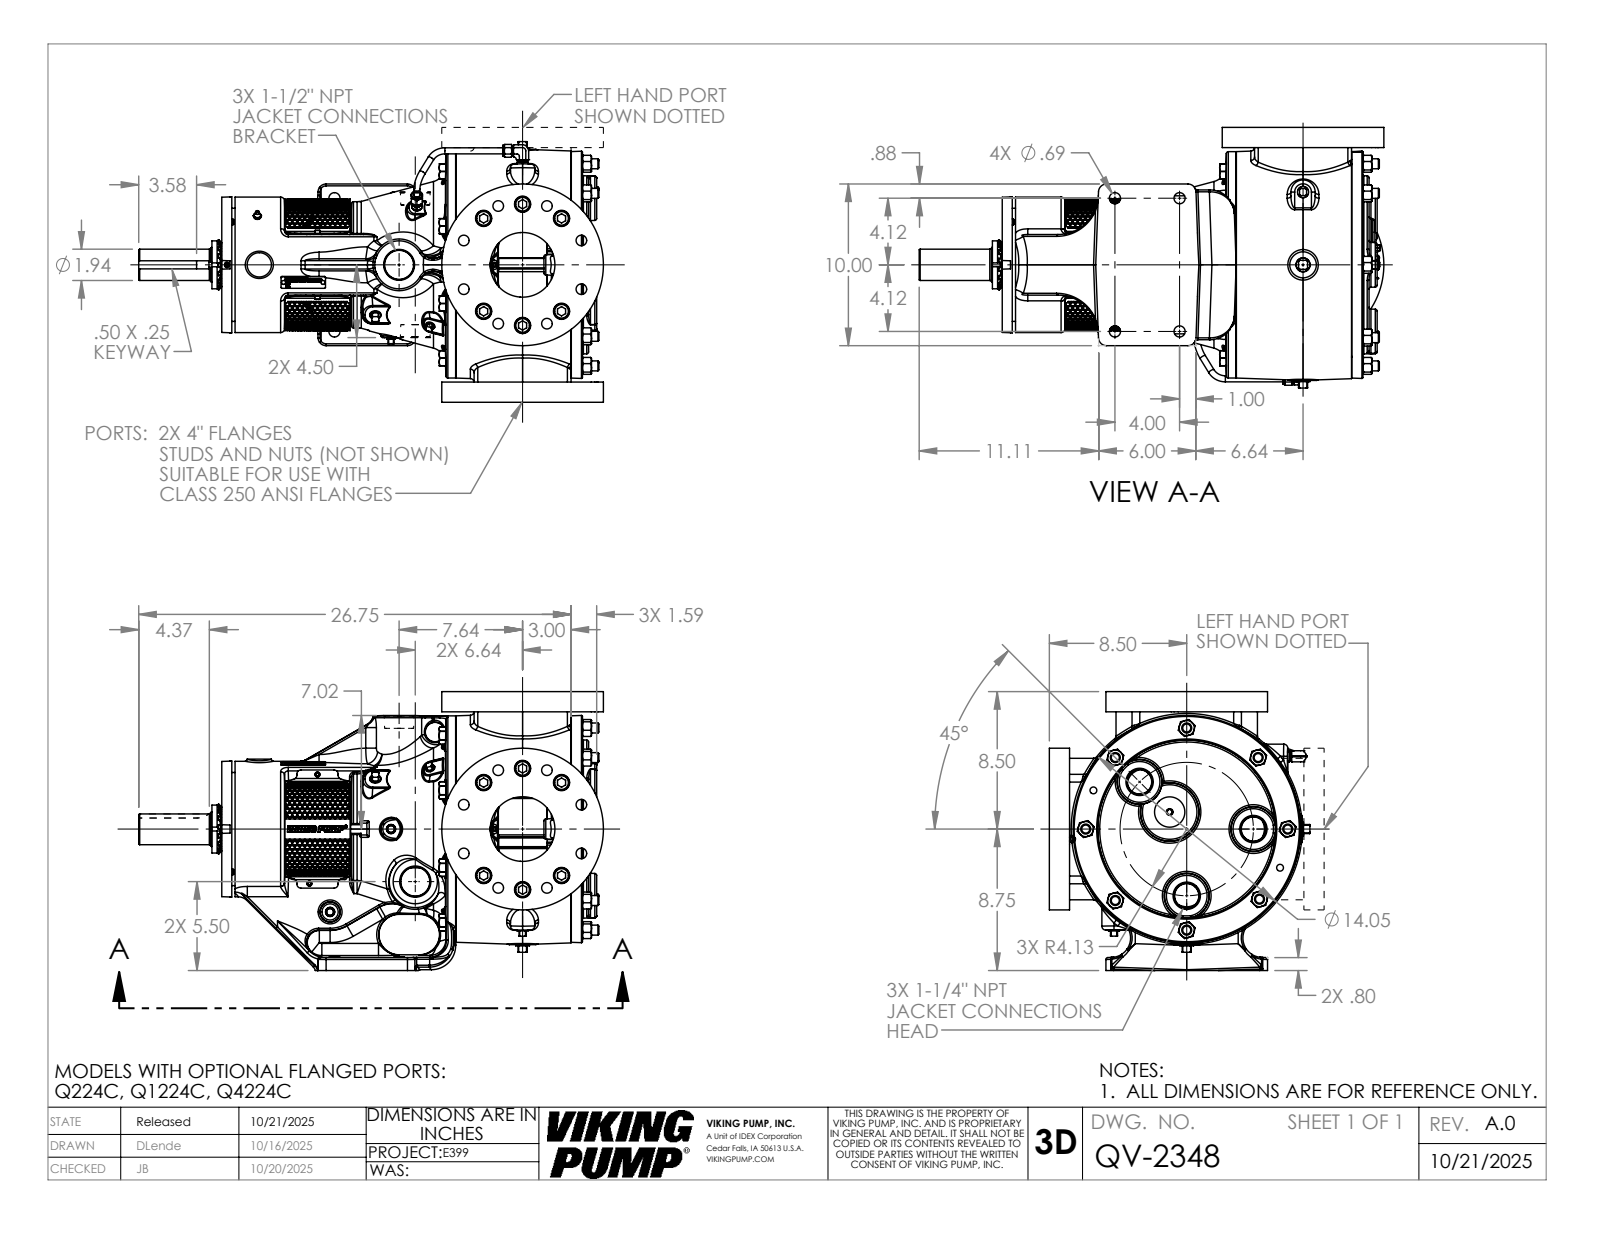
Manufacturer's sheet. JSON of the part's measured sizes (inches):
{"part_name": "QV-2348", "step_written_by": "SolidWorks 2024 (AUTOMOTIVE_DESIGN)", "units": "inches", "bodies": {"solids": 1, "faces": 3965, "planar": 1361, "cylindrical": 658, "other": 1946}, "overall_size": [28.751, 17.25, 16.221], "volume_in3": 2432, "surface_area_in2": 2170, "round_holes": [[0.656, 16], [1, 12], [0.25, 9], [0.266, 8], [1.157, 8], [0.688, 4], [0.159, 2], [0.313, 2], [0.422, 2], [4, 2], [0.453, 1], [2.157, 1]], "round_bosses_or_shafts": [[0.937, 12], [0.617, 8], [0.375, 4], [0.312, 3], [0.19, 3], [10, 2], [0.687, 2], [0.563, 2]], "partial_cylinders_radius": [[0.12, 54], [0.75, 24], [0.015, 18], [0.092, 18], [0.07, 16], [0.5, 12], [0.24, 10], [0.25, 10]], "face_to_face_distances": [1.25, 17.25, 0.38, 22.317, 22.698, 16, 3.82, 18.498, 18.878, 7.972], "hole_center_spacings": [3.75, 7.276, 2.079, 3.937, 5.783, 1.184, 2.713, 3.013]}
